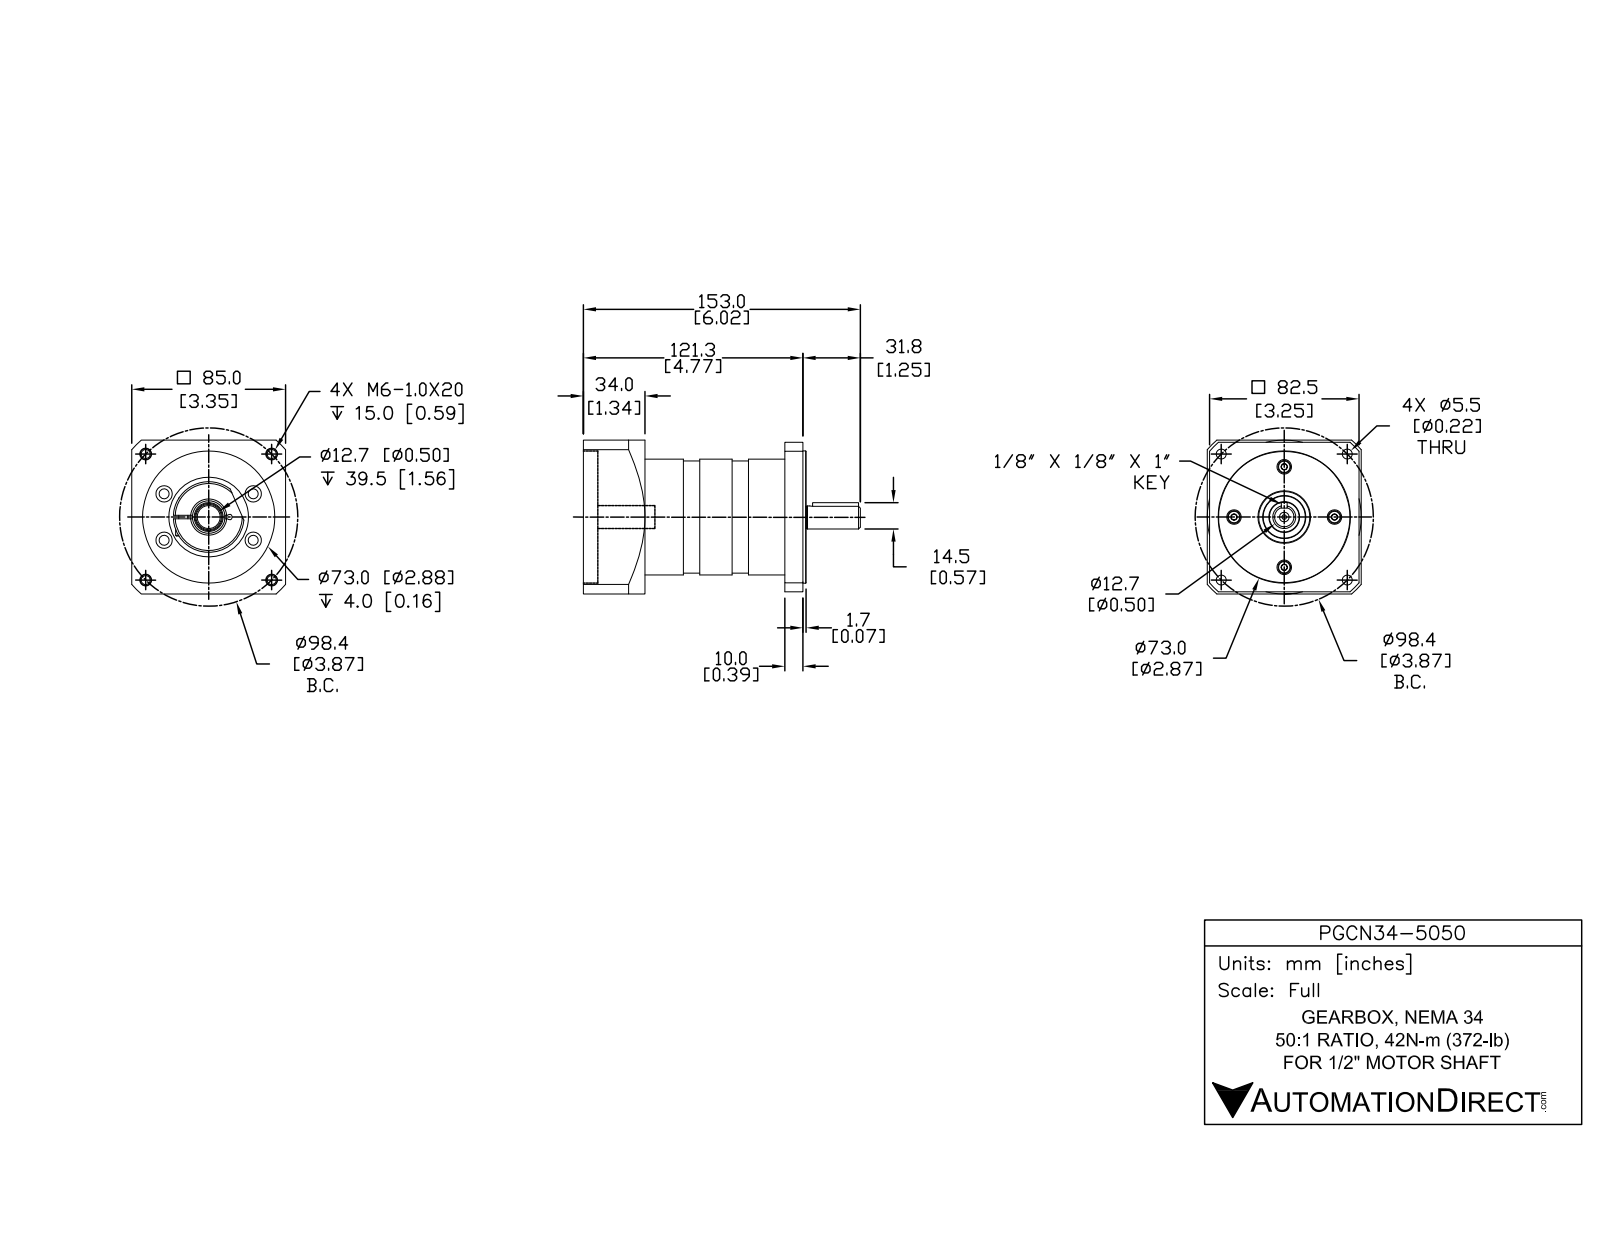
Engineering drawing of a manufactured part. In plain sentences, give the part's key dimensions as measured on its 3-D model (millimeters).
The part is named "Bushing_.5x14x20.5; N34-A06; PE-N34-II 14mm Input; PGCN34-5050". Its 3-D file was written by "SolidWorks 2014 (AUTOMOTIVE_DESIGN)". It is 3 solids with 368 faces: 108 planar, 146 cylindrical and 114 other. Overall it measures 153.1 by 85 by 85 millimeters. Its volume is 501 400 cubic millimeters and its surface area 75 610 square millimeters. Round holes: 5 of diameter 5, 5 of diameter 9, 4 of diameter 3.3, 4 of diameter 4, 4 of diameter 5.5, 4 of diameter 5.5, 4 of diameter 6, 4 of diameter 8, 2 of diameter 14, 1 of diameter 2.5, 1 of diameter 12.7, 1 of diameter 28.2. Round bosses or shafts: 4 of diameter 7, 1 of diameter 73, 1 of diameter 64, 1 of diameter 62, 1 of diameter 39, 1 of diameter 23.8, 1 of diameter 23.3, 1 of diameter 20. Partial cylindrical surfaces (rounded edges, fillets, slot ends): 1 of radius 1.5, 1 of radius 1.6, 1 of radius 9, 1 of radius 55, 1 of radius 56.5. The main face-to-face distances are 85, 11.8, 123, 111.3, 10, 34, 87.3, 33, 78.3, 1.8. The hole center spacings are 35.5, 71.6, 13.2, 24.2, 27.7, 27.8, 28.8, 39.2.
